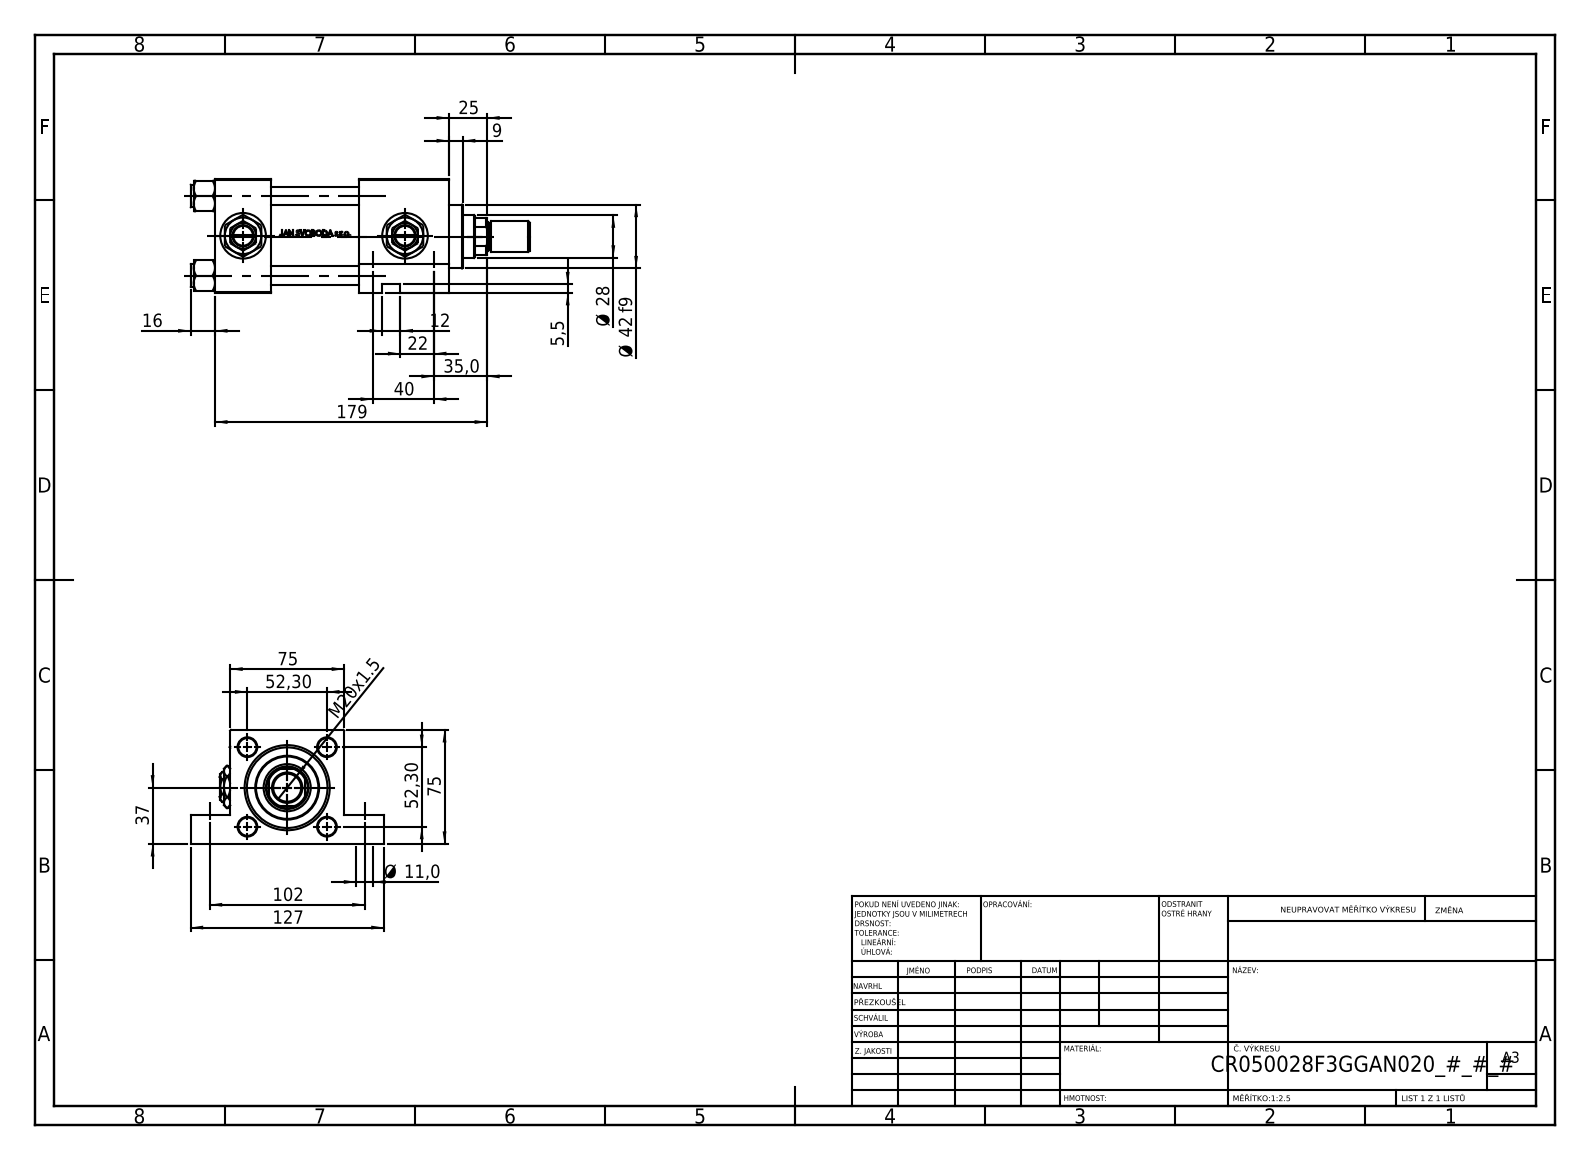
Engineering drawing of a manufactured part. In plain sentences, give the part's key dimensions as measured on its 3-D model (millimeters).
The part is named "NUT_M5_F; V215CR_F_TYCINKA; ROD_END_AH; V215CR_F_Body (+3 more)". Its 3-D file was written by "SolidWorks 2019 (CONFIG_CONTROL_DESIGN)". It is 14 solids with 1216 faces: 488 planar, 140 cylindrical and 588 other. Overall it measures 223 by 127 by 75 millimeters. Its volume is 721 579 cubic millimeters and its surface area 166 849 square millimeters. Round holes: 4 of diameter 12, 4 of diameter 20.96, 4 of diameter 30, 3 of diameter 7, 2 of diameter 11, 2 of diameter 11, 1 of diameter 18.5, 1 of diameter 28, 1 of diameter 31, 1 of diameter 41, 1 of diameter 50, 1 of diameter 53. Round bosses or shafts: 4 of diameter 15, 1 of diameter 56, 1 of diameter 42, 1 of diameter 20, 1 of diameter 18. Partial cylindrical surfaces (rounded edges, fillets, slot ends): 1 of radius 13.5. The main face-to-face distances are 75, 37, 154, 117, 58, 95, 59, 19, 56, 74.8. The hole center spacings are 52.3, 36.63, 37.34, 40, 51.62, 60.21, 73.96, 99.56.
